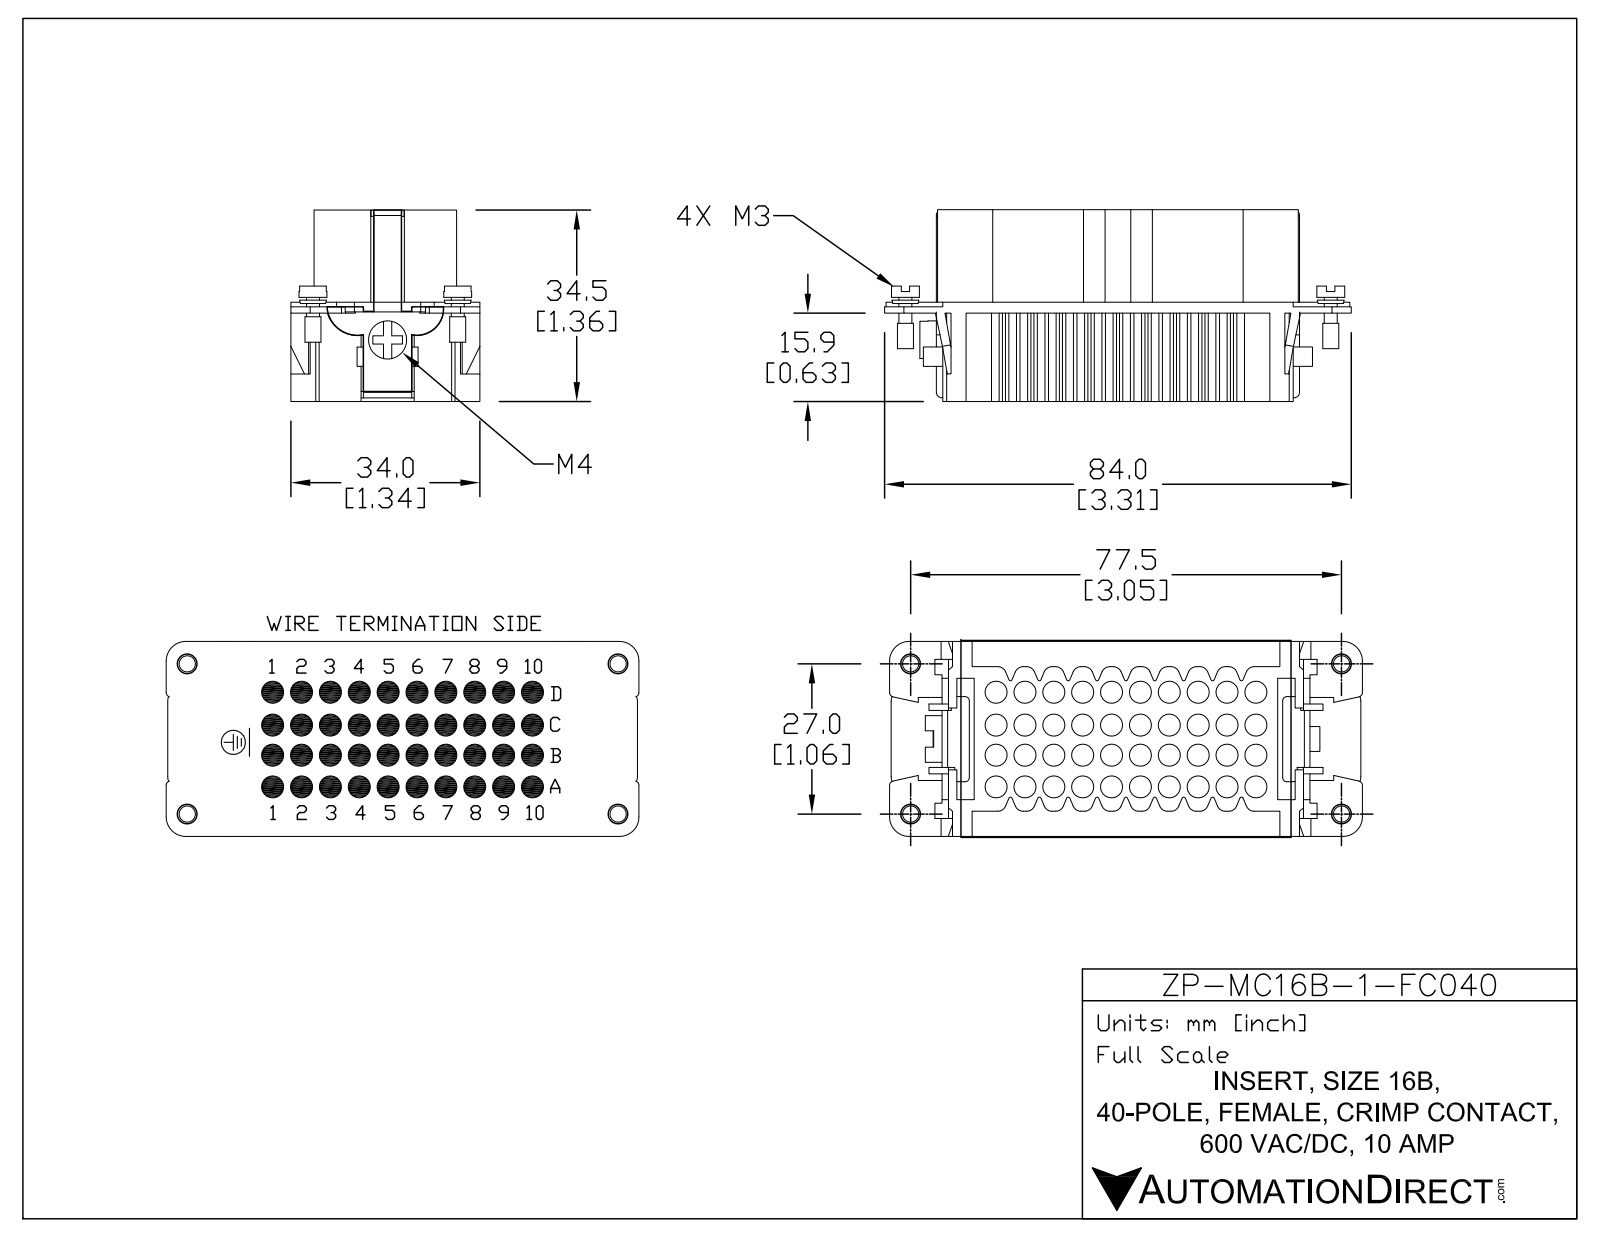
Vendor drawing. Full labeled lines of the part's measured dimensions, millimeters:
Part name (STEP PRODUCT): ZP-MC16B-1-FC040
STEP written by: SolidWorks 2021 (CONFIG_CONTROL_DESIGN)
Units: millimetres
Bodies: 1 solid, 2128 faces (983 planar, 516 cylindrical, 629 other)
Overall size (bounding box): 84.3 × 34.6 × 33.6
Volume: 51 520 mm³ · Surface area: 18 570 mm²
Round holes (diameter × count): ⌀2.7 ×4, ⌀4 ×1
Round bosses / shafts (diameter × count): ⌀5.4 ×4, ⌀5.2 ×4, ⌀3 ×4, ⌀2.3 ×4, ⌀7 ×1, ⌀5 ×1, ⌀3.6 ×1
Partial cylindrical surfaces — rounded edges, fillets, slot ends (radius × count): R0.2 ×94, R0.5 ×77, R0.3 ×56, R1.5 ×48, R1 ×18, R0.8 ×8, R0.3 ×4, R0.3 ×4
Main face-to-face distances: 16.4, 17.4, 1.2, 18.1, 15.9, 2.2, 14.6, 0.7, 19.9, 19.2
Hole centre spacings: 27, 77.5, 82.1
